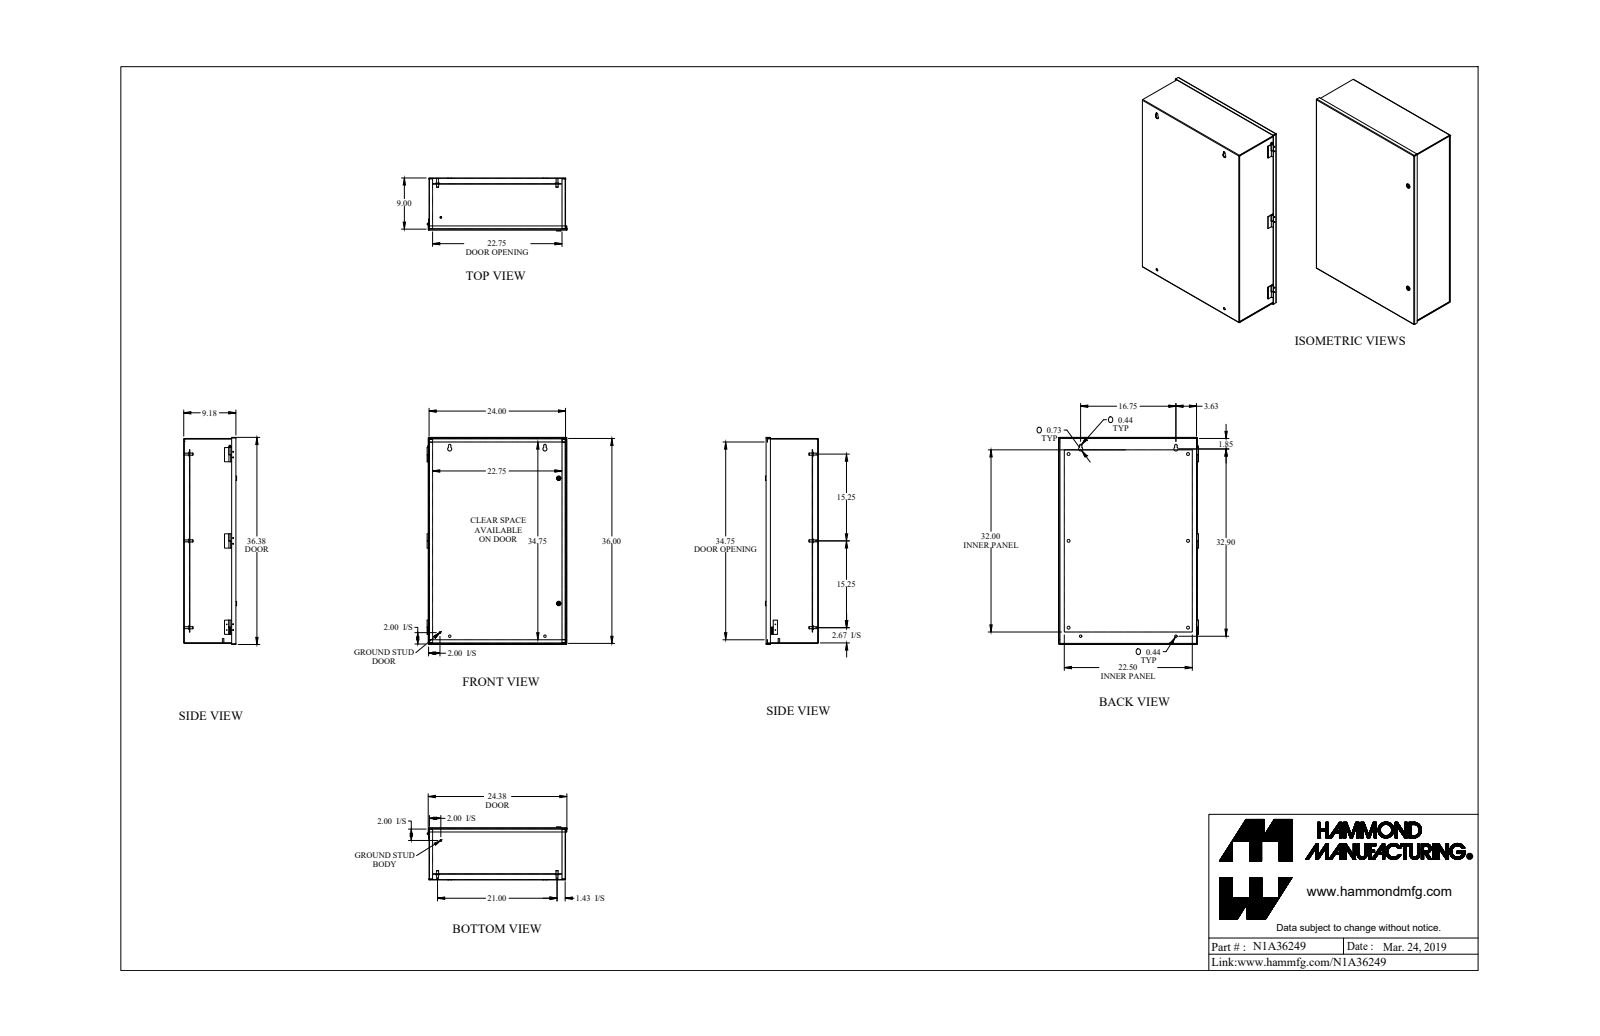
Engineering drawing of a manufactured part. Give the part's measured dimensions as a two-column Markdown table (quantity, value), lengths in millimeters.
| quantity | value |
| --- | --- |
| part name | N1A36249 |
| STEP written by | SolidWorks 2018 (AUTOMOTIVE_DESIGN) |
| units | millimeters |
| bodies | 34 solids, 767 faces (434 planar, 269 cylindrical, 64 other) |
| overall size | 924.2 × 624.2 × 236.2 |
| volume | 4 475 000 mm³ |
| surface area | 4 905 000 mm² |
| round holes (diameter × count) | 3.6 × 12, 12.7 × 6, 7.8 × 4, 11.3 × 4, 11.1 × 2, 13.1 × 2, 18.6 × 2, 4.3 × 1, 4.7 × 1 |
| round bosses / shafts (diameter × count) | 3.3 × 12, 9.5 × 7, 16.5 × 6, 8.4 × 6, 25.4 × 4, 20 × 2, 13.6 × 2, 12.6 × 2 |
| partial cylindrical surfaces (radius × count) | 0.9 × 16, 2.7 × 16, 1.5 × 2, 3.2 × 2, 3.9 × 2, 5.6 × 2, 8 × 2, 0.8 × 1 |
| main face-to-face distances | 1.8, 231.3, 25.6, 205.6, 229.4, 233.1, 23.8, 27.5, 203.8, 207.5 |
| hole center spacings | 25.4, 28.4, 385, 387.4, 659.2, 533.4, 108.2, 279.5 |
